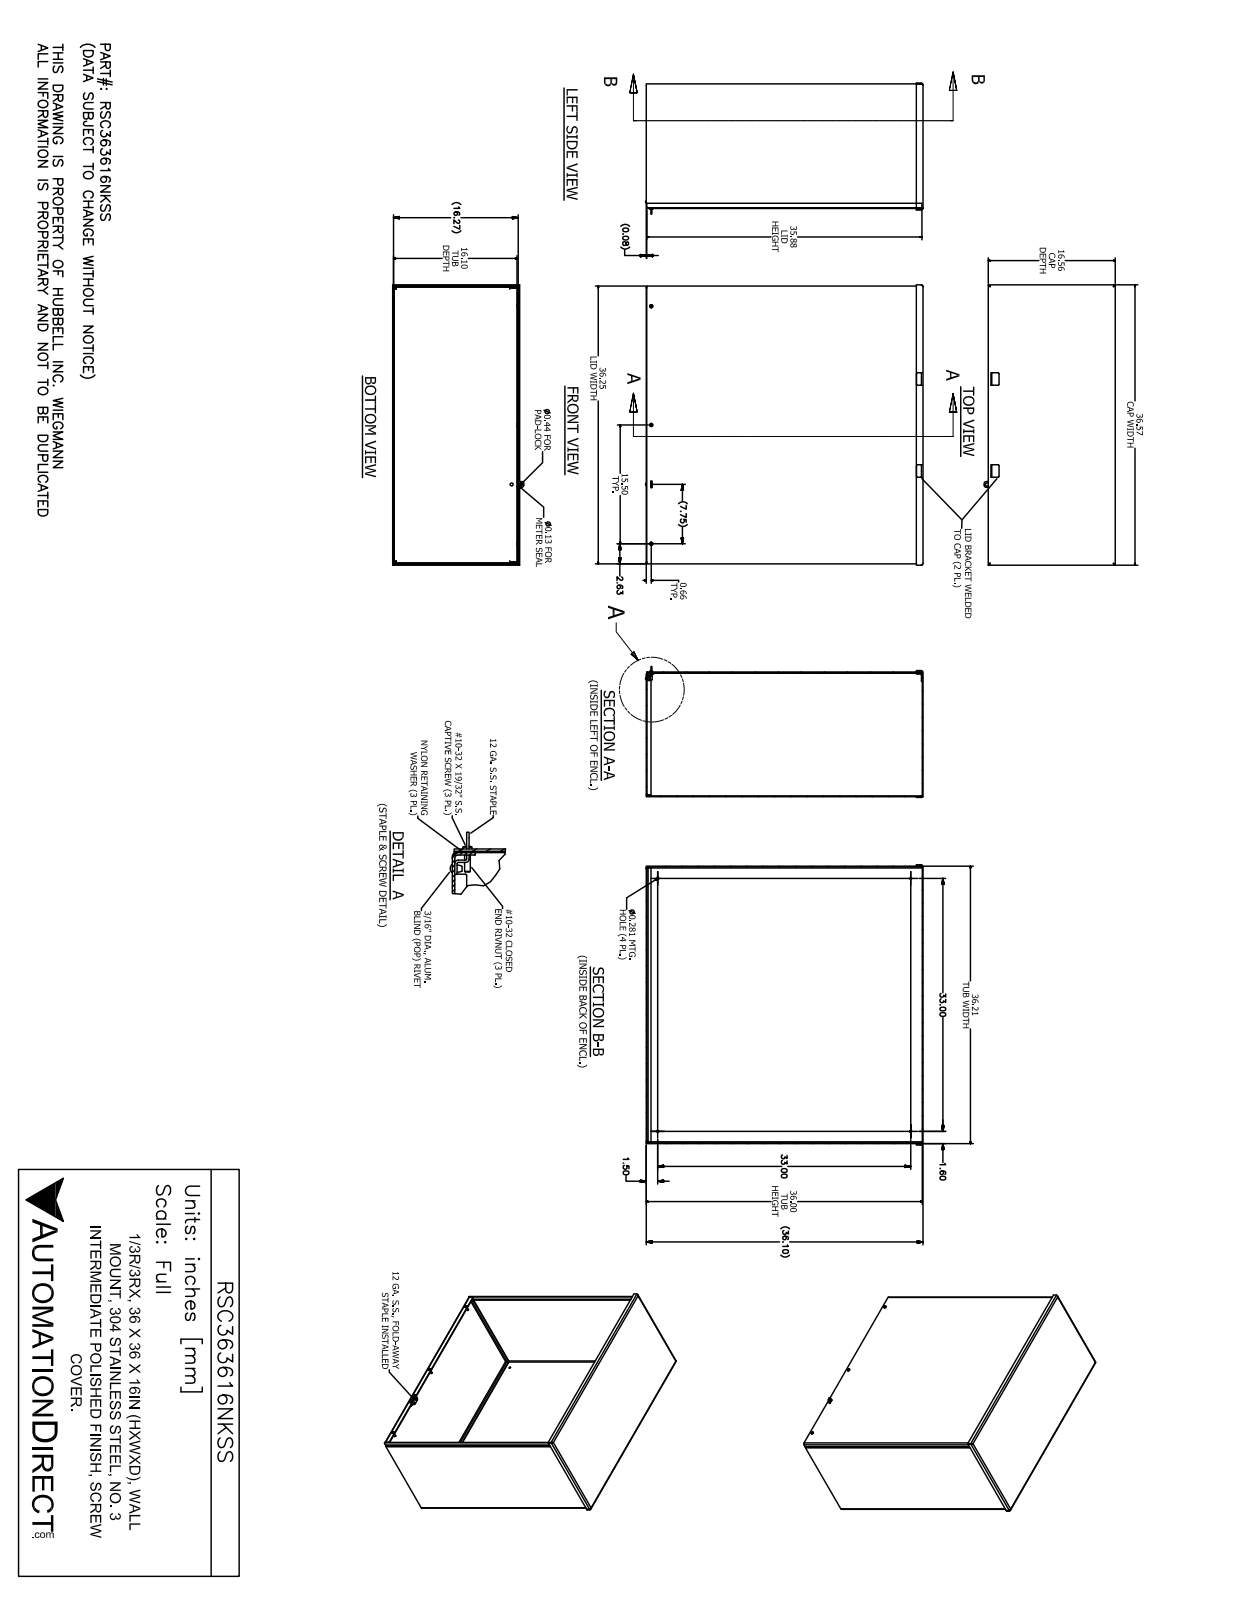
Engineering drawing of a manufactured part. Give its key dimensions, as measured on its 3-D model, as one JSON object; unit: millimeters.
{"part_name": "RSC363616NKSS", "step_written_by": "SolidWorks 2017 (AUTOMOTIVE_DESIGN)", "units": "millimeters", "bodies": {"solids": 17, "faces": 440, "planar": 241, "cylindrical": 117, "other": 82}, "overall_size": [928.9, 919.3, 434.2], "volume_mm3": 8703000, "surface_area_mm2": 6633000, "round_holes": [[6.4, 6], [7.1, 4], [4, 3], [5, 3], [6.5, 3], [7.1, 3], [3.2, 1], [5, 1], [5.1, 1], [11.1, 1]], "round_bosses_or_shafts": [[11.5, 3], [10.3, 3], [6.3, 3], [4.2, 3], [4.7, 1]], "partial_cylinders_radius": [[3.6, 14], [6.2, 14], [3.2, 9], [0.8, 6], [6.4, 4], [2.3, 3], [1.2, 2], [1.6, 2]], "face_to_face_distances": [2.6, 410.5, 914.4, 917, 413.2, 407.9, 911.8, 919.7, 914.2, 2.8], "hole_center_spacings": [393.7, 838.2, 965.8, 881.9, 33.2, 33.8, 419.7, 419.7]}
